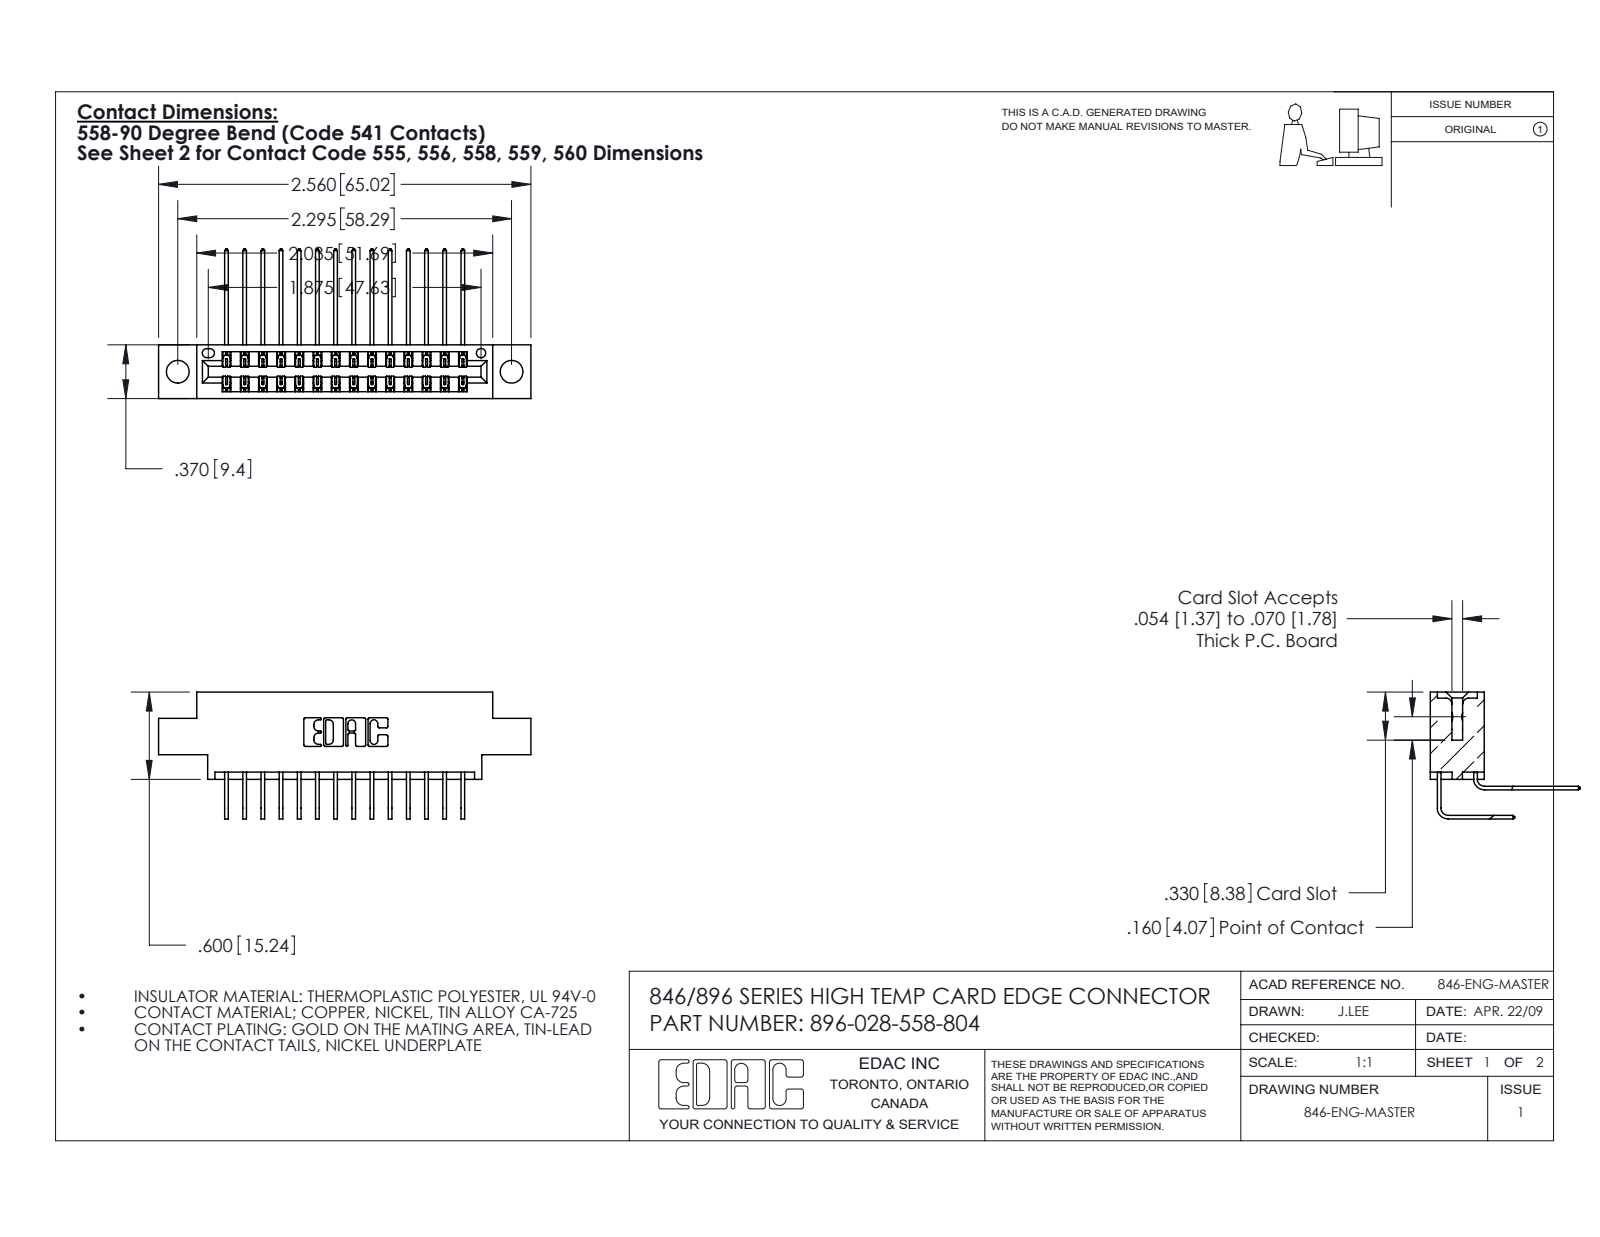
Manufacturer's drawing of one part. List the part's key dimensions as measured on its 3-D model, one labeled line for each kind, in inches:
Part name (STEP PRODUCT): 345-292-001_558 Tail - 2; 346 Part_0.170 Offset - 0.156 Dia-TH; 396-028-558-804; 345-292-001_558 559 Tail - 1
STEP written by: SolidWorks 2016 (CONFIG_CONTROL_DESIGN)
Units: inches
Bodies: 29 solids, 1638 faces (1116 planar, 522 cylindrical, 0 other)
Overall size (bounding box): 2.56 × 1.03 × 0.873
Volume: 0.369 in³ · Surface area: 13.38 in²
Round holes (diameter × count): ⌀0.156 ×2, ⌀0.064 ×1
Partial cylindrical surfaces — rounded edges, fillets, slot ends (radius × count): R0.006 ×42, R0.01 ×22, R0.007 ×6, R0.031 ×6, R0.026 ×3, R0.014 ×2, R0.022 ×2, R0.024 ×2
Main face-to-face distances: 0.048, 0.322, 0.37, 0.25, 0.025, 0.072, 0.298, 0.275, 0.148, 0.222
Hole centre spacings: 0.246, 2.089, 2.295
